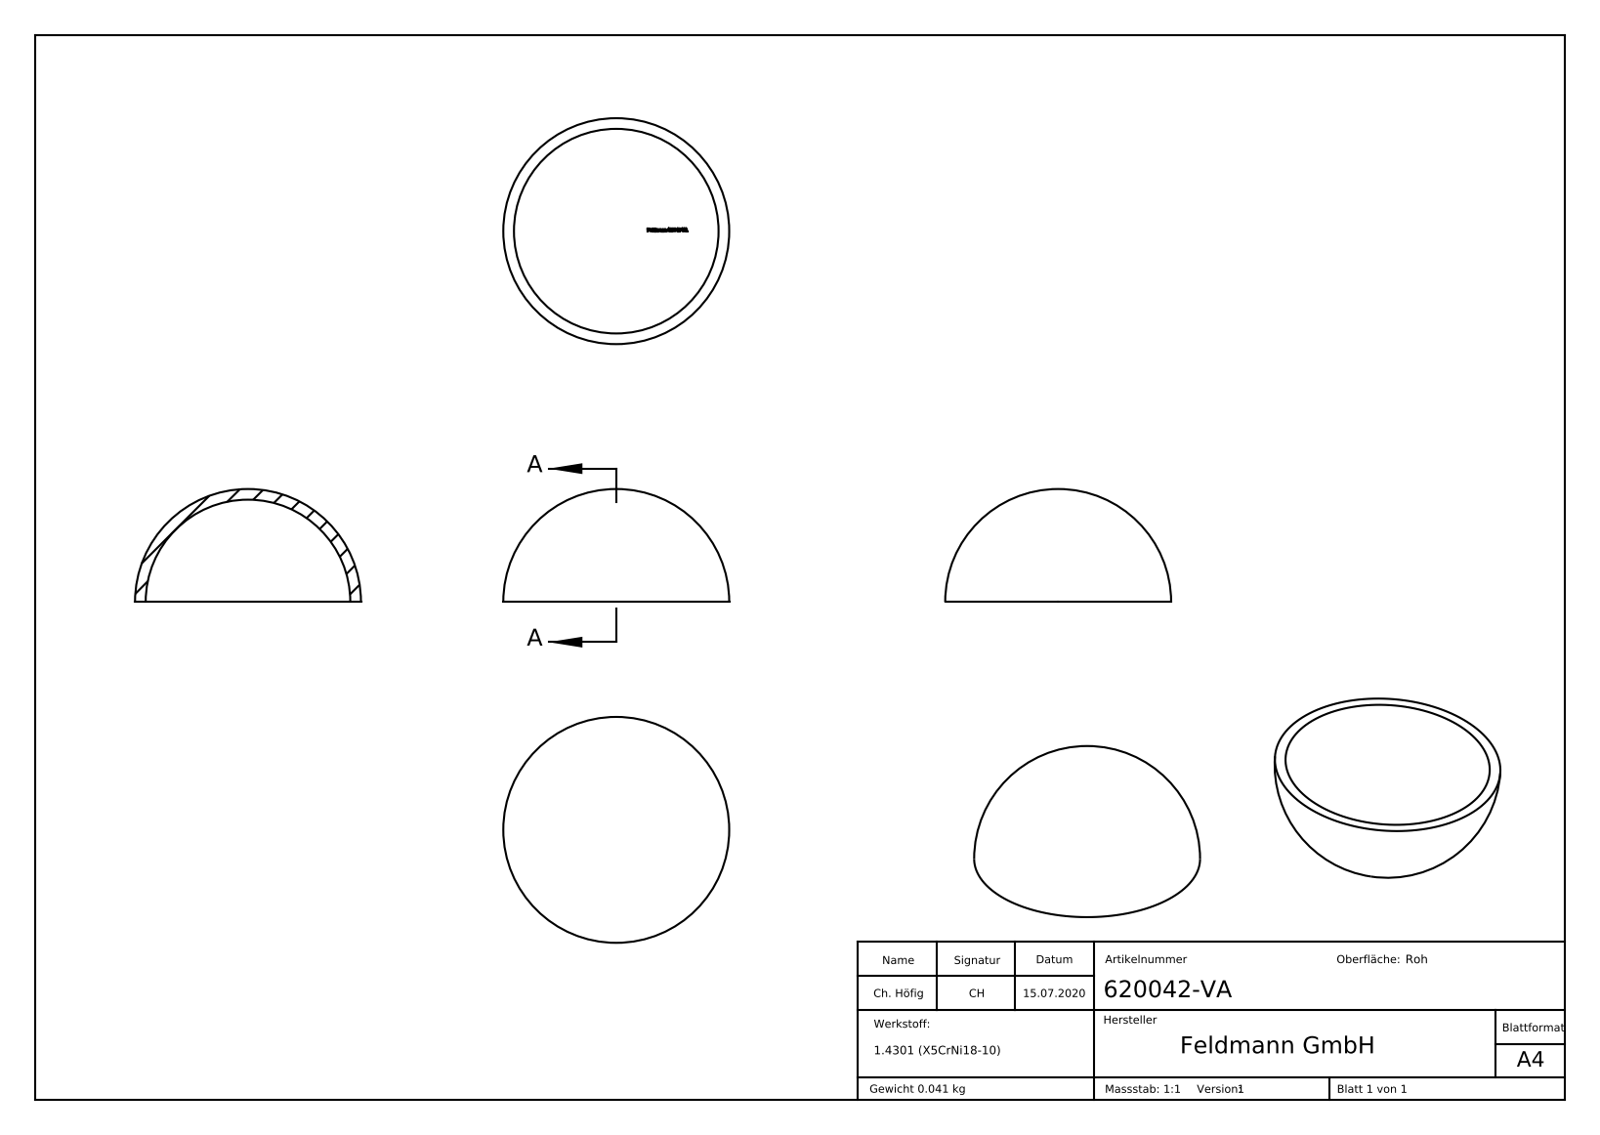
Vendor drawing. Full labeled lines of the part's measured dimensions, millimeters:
Part name (STEP PRODUCT): 620042-VA
STEP written by: SolidWorks 2018 (CONFIG_CONTROL_DESIGN)
Units: millimetres
Bodies: 1 solid, 219 faces (105 planar, 0 cylindrical, 114 other)
Overall size (bounding box): 42.4 × 42.4 × 21.2
Volume: 5 132 mm³ · Surface area: 5 399 mm²
Main face-to-face distances: 1.19, 0.45, 3.1, 4.79, 2.65, 0.61, 0.53, 2.54, 0.55, 0.31
